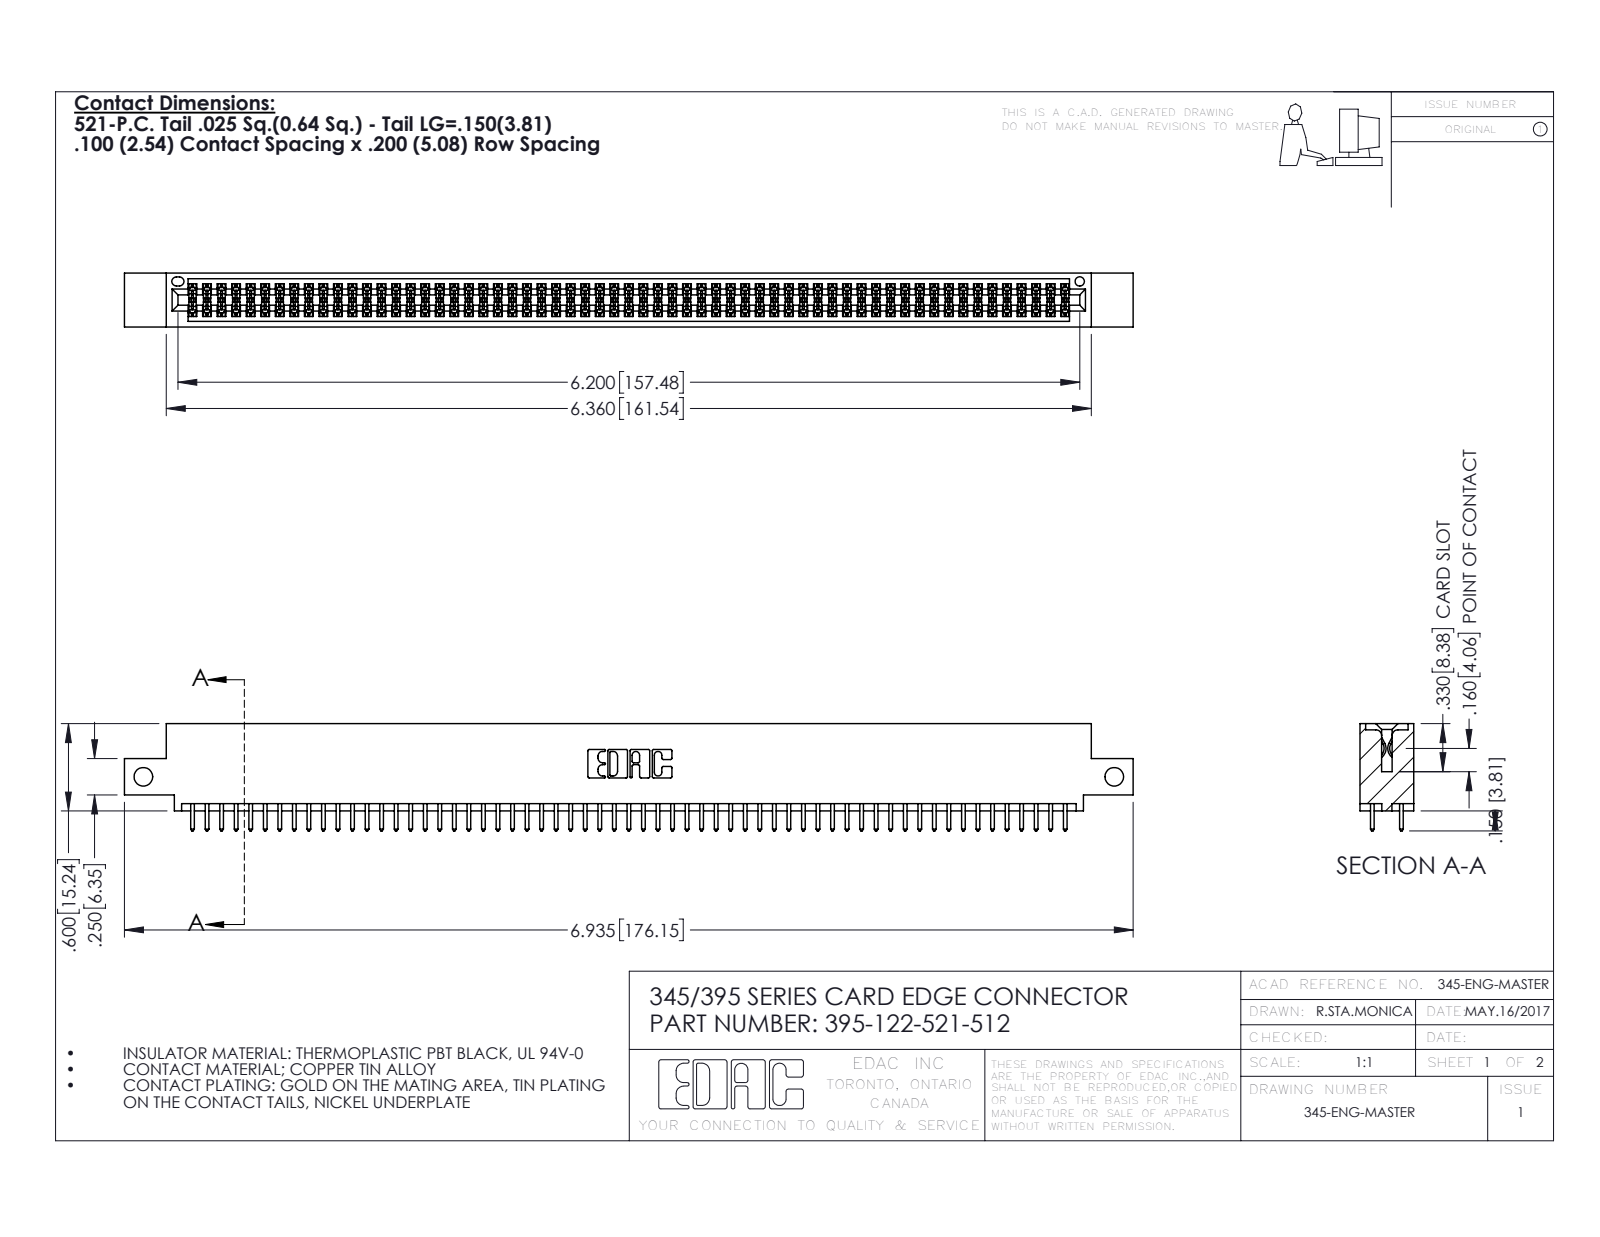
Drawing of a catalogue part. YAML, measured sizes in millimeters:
part_name: "345 Part_0.110 Offset - Side Mount; 395-122-521-512; 345-292-001_345-293-121"
step_written_by: "SolidWorks 2016 (CONFIG_CONTROL_DESIGN)"
units: millimeters
bodies: {solids: 123, faces: 6230, planar: 4110, cylindrical: 2120, other: 0}
overall_size: [176.1, 18.7, 9.4]
volume: 17080
surface_area: 25250
round_holes:
  - {diameter: 3.3, count: 2}
  - {diameter: 1.6, count: 1}
partial_cylinders:
  - {radius: 0.2, count: 183}
  - {radius: 0.3, count: 122}
  - {radius: 0.3, count: 22}
  - {radius: 0.2, count: 6}
  - {radius: 0.8, count: 6}
  - {radius: 0.7, count: 3}
  - {radius: 0.4, count: 2}
  - {radius: 0.5, count: 2}
face_to_face_distances: [7.6, 1.8, 5.1, 2.5, 6.9, 0.6, 9.4, 5.7, 4.4, 3.8]
hole_center_spacings: [169.5]
